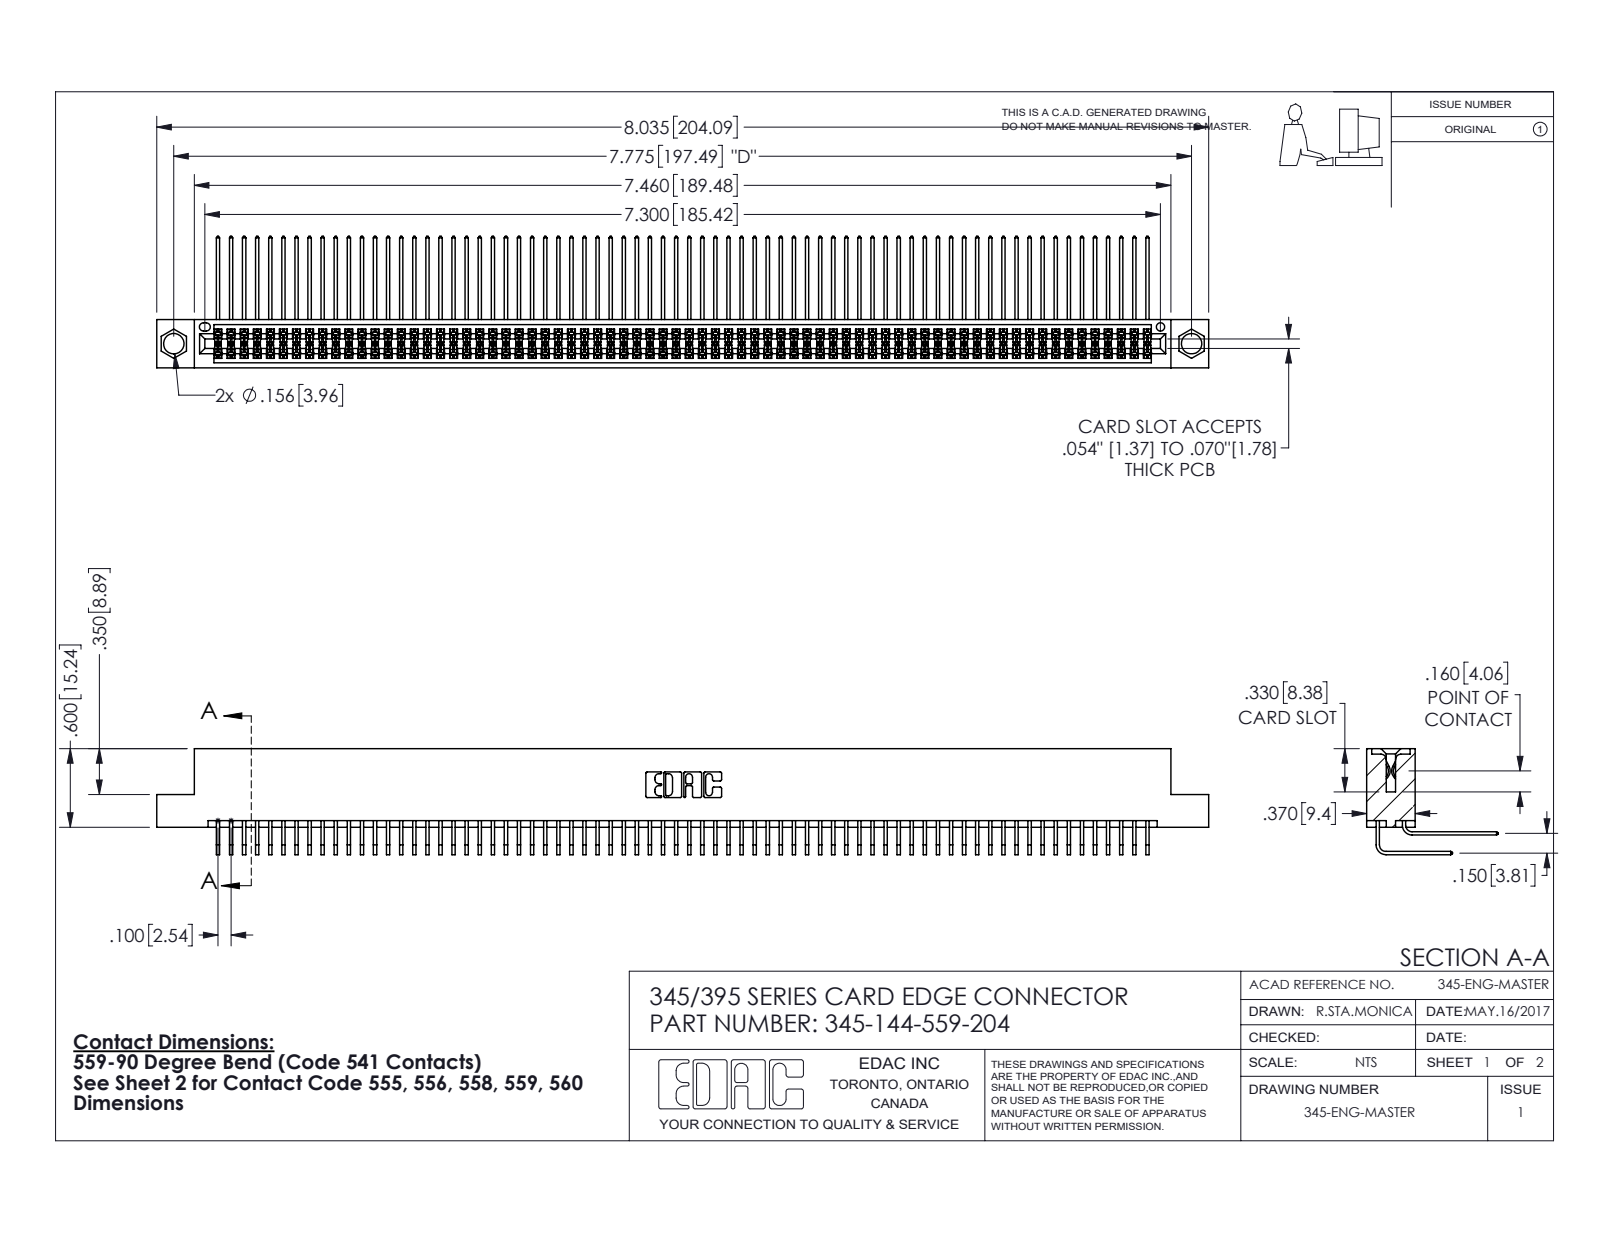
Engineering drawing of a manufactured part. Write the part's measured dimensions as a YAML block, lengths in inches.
part_name: "345-292-001_558 559 Tail - 1; 345 Part_Flush Mounting Lugs - 0.156 Dia-TI; 345-292-001_559 Tail - 2; 345-144-559-204"
step_written_by: "SolidWorks 2020 (CONFIG_CONTROL_DESIGN)"
units: inches
bodies: {solids: 145, faces: 7628, planar: 5134, cylindrical: 2494, other: 0}
overall_size: [8.035, 1.005, 0.809]
volume: 1.271
surface_area: 54.45
round_holes:
  - {diameter: 0.156, count: 2}
  - {diameter: 0.064, count: 1}
partial_cylinders:
  - {radius: 0.006, count: 288}
  - {radius: 0.01, count: 22}
  - {radius: 0.007, count: 6}
  - {radius: 0.031, count: 6}
  - {radius: 0.026, count: 3}
  - {radius: 0.014, count: 2}
  - {radius: 0.019, count: 2}
  - {radius: 0.022, count: 2}
face_to_face_distances: [0.072, 0.298, 0.2, 0.37, 0.098, 0.272, 0.025, 0.225, 0.175, 0.15]
hole_center_spacings: [0.27, 7.539, 7.775]
